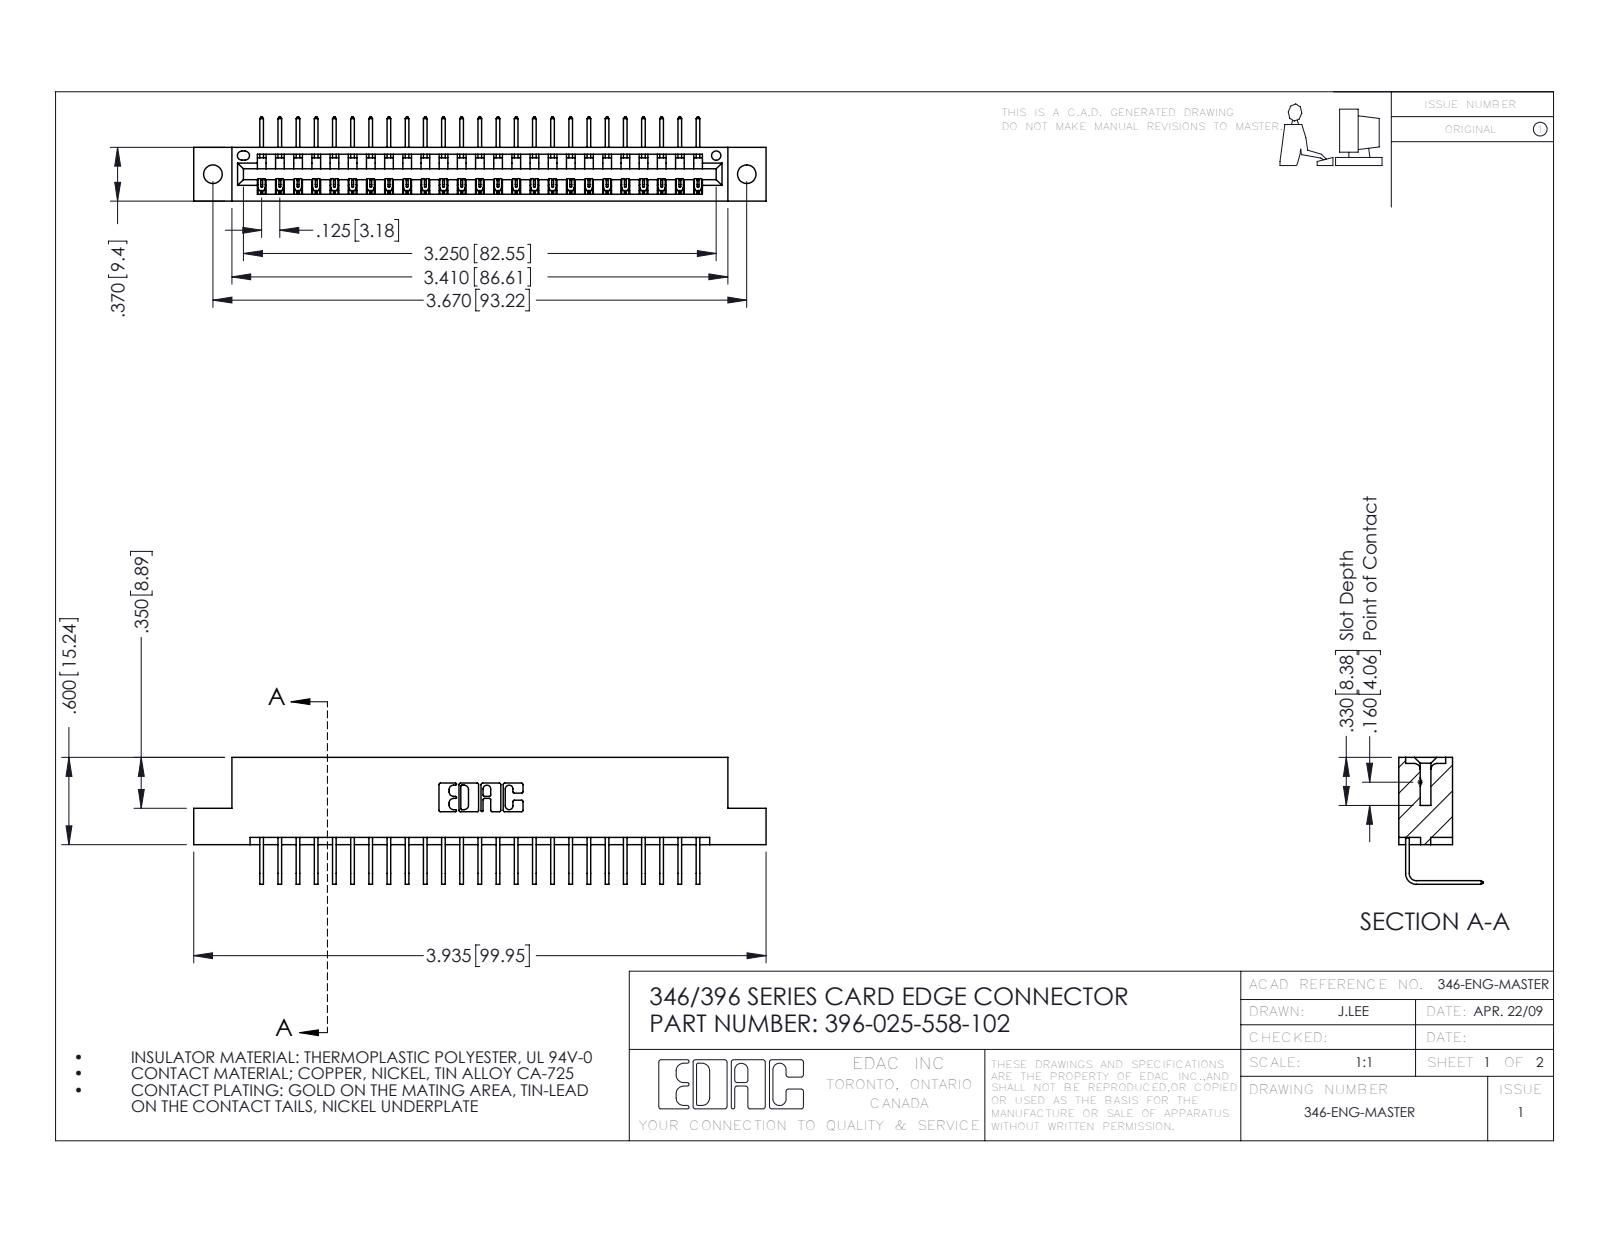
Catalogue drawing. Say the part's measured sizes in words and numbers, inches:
The part is named "396-025-558-102; 345-292-001_558 Tail - 2; 346 Part_Flush Mounting Lugs - 0.128 Dia". Its 3-D file was written by "SolidWorks 2016 (CONFIG_CONTROL_DESIGN)". It is 26 solids with 1622 faces: 1126 planar, 496 cylindrical and 0 other. Overall it measures 3.935 by 0.873 by 0.58 inches. Its volume is 0.58 cubic inches and its surface area 18.46 square inches. Round holes: 2 of diameter 0.128, 1 of diameter 0.064. Partial cylindrical surfaces (rounded edges, fillets, slot ends): 50 of radius 0.006, 22 of radius 0.01, 6 of radius 0.007, 6 of radius 0.031, 3 of radius 0.026, 2 of radius 0.031, 2 of radius 0.04, 1 of radius 0.014. The main face-to-face distances are 0.322, 0.048, 0.37, 0.25, 0.298, 0.025, 0.072, 0.148, 0.222, 0.1. The hole center spacings are 0.246, 3.462, 3.67.
